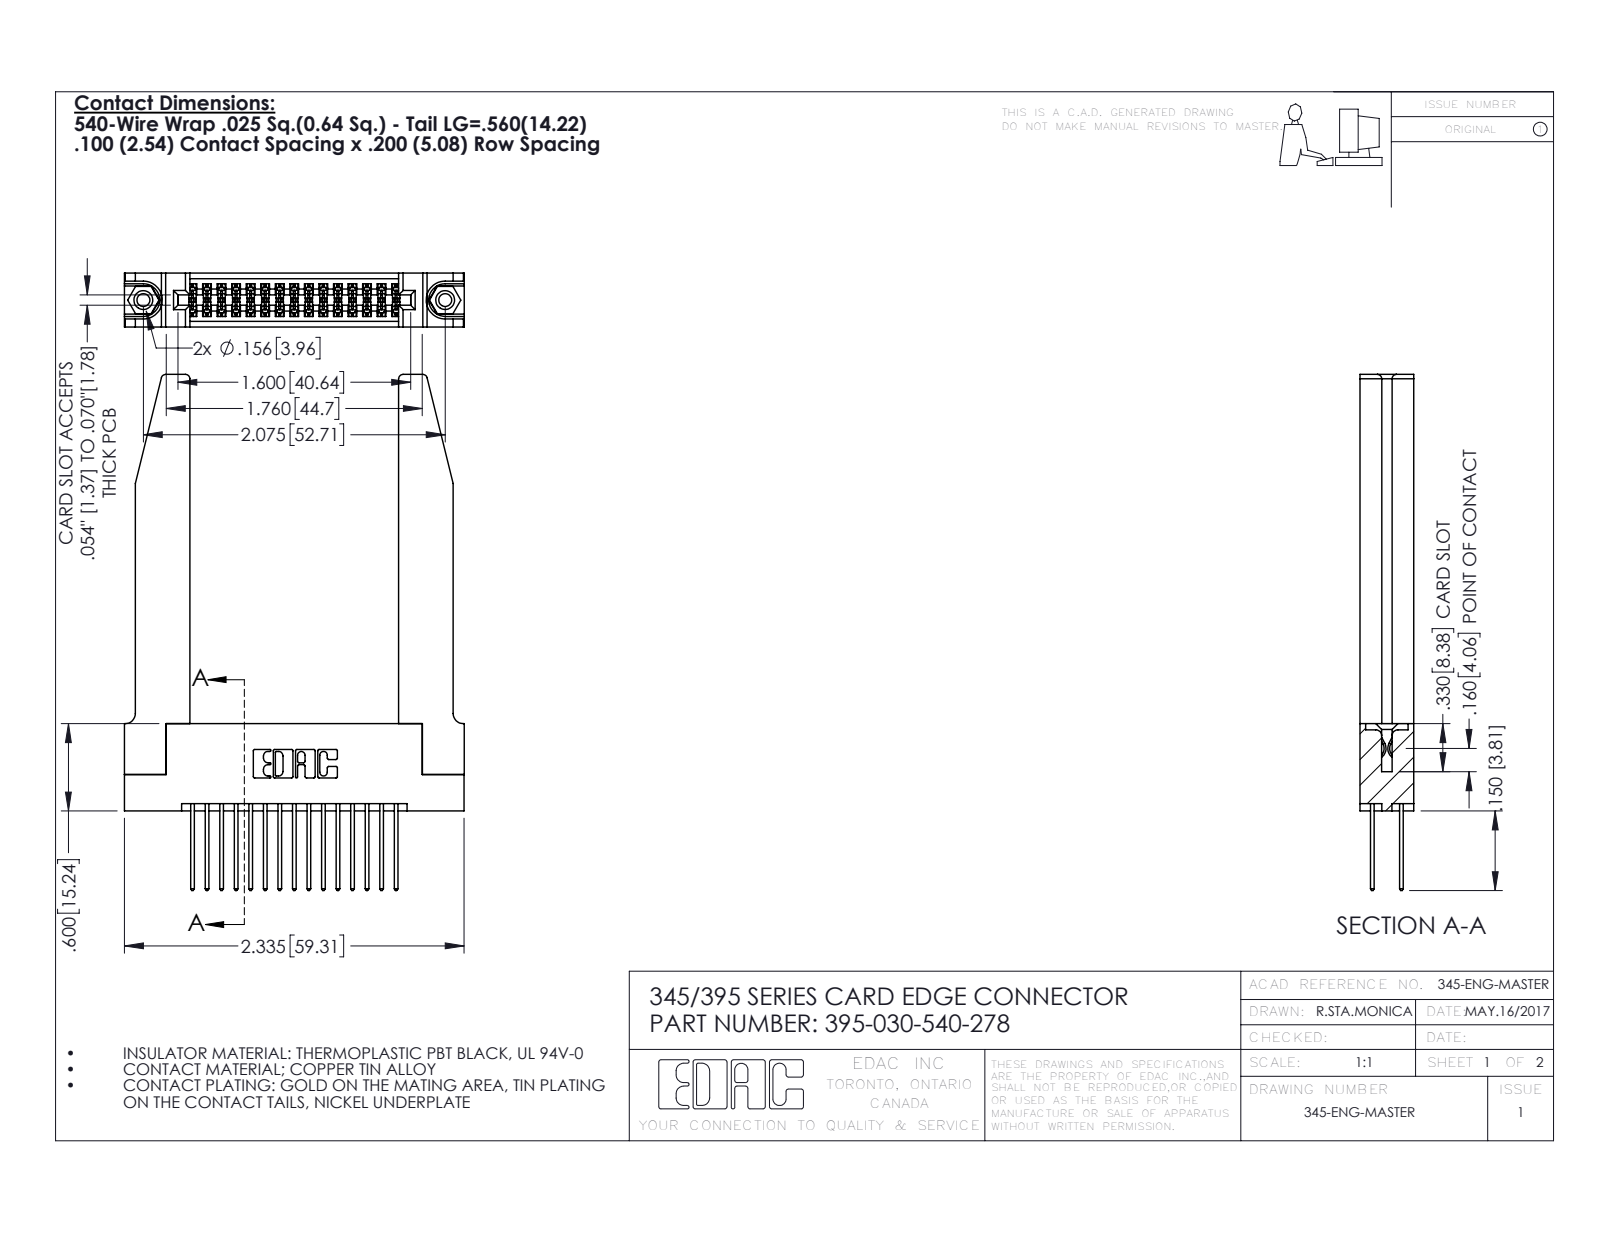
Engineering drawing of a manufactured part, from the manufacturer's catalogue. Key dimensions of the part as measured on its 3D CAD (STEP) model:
Part name (STEP PRODUCT): 345-292-001_345-293-140; 345-220-078_345-220-078; 395-030-540-278; 345 Part_Flush Mounting Lugs - 0.156 Dia-TH (+1 more)
STEP written by: SolidWorks 2016 (CONFIG_CONTROL_DESIGN)
Units: inches
Bodies: 35 solids, 1860 faces (1212 planar, 596 cylindrical, 52 other)
Overall size (bounding box): 3.547 × 2.336 × 0.37
Volume: 0.818 in³ · Surface area: 23.5 in²
Round holes (diameter × count): ⌀0.089 ×2, ⌀0.125 ×2, ⌀0.156 ×2, ⌀0.064 ×1
Round bosses / shafts (diameter × count): ⌀0.155 ×2
Partial cylindrical surfaces — rounded edges, fillets, slot ends (radius × count): R0.006 ×45, R0.01 ×30, R0.01 ×22, R0.03 ×8, R0.007 ×6, R0.031 ×6, R0.026 ×3, R0.014 ×2
Main face-to-face distances: 0.37, 0.072, 0.298, 0.2, 0.098, 0.272, 0.025, 0.225, 0.15, 0.148
Hole centre spacings: 0.27, 1.842, 2.075
